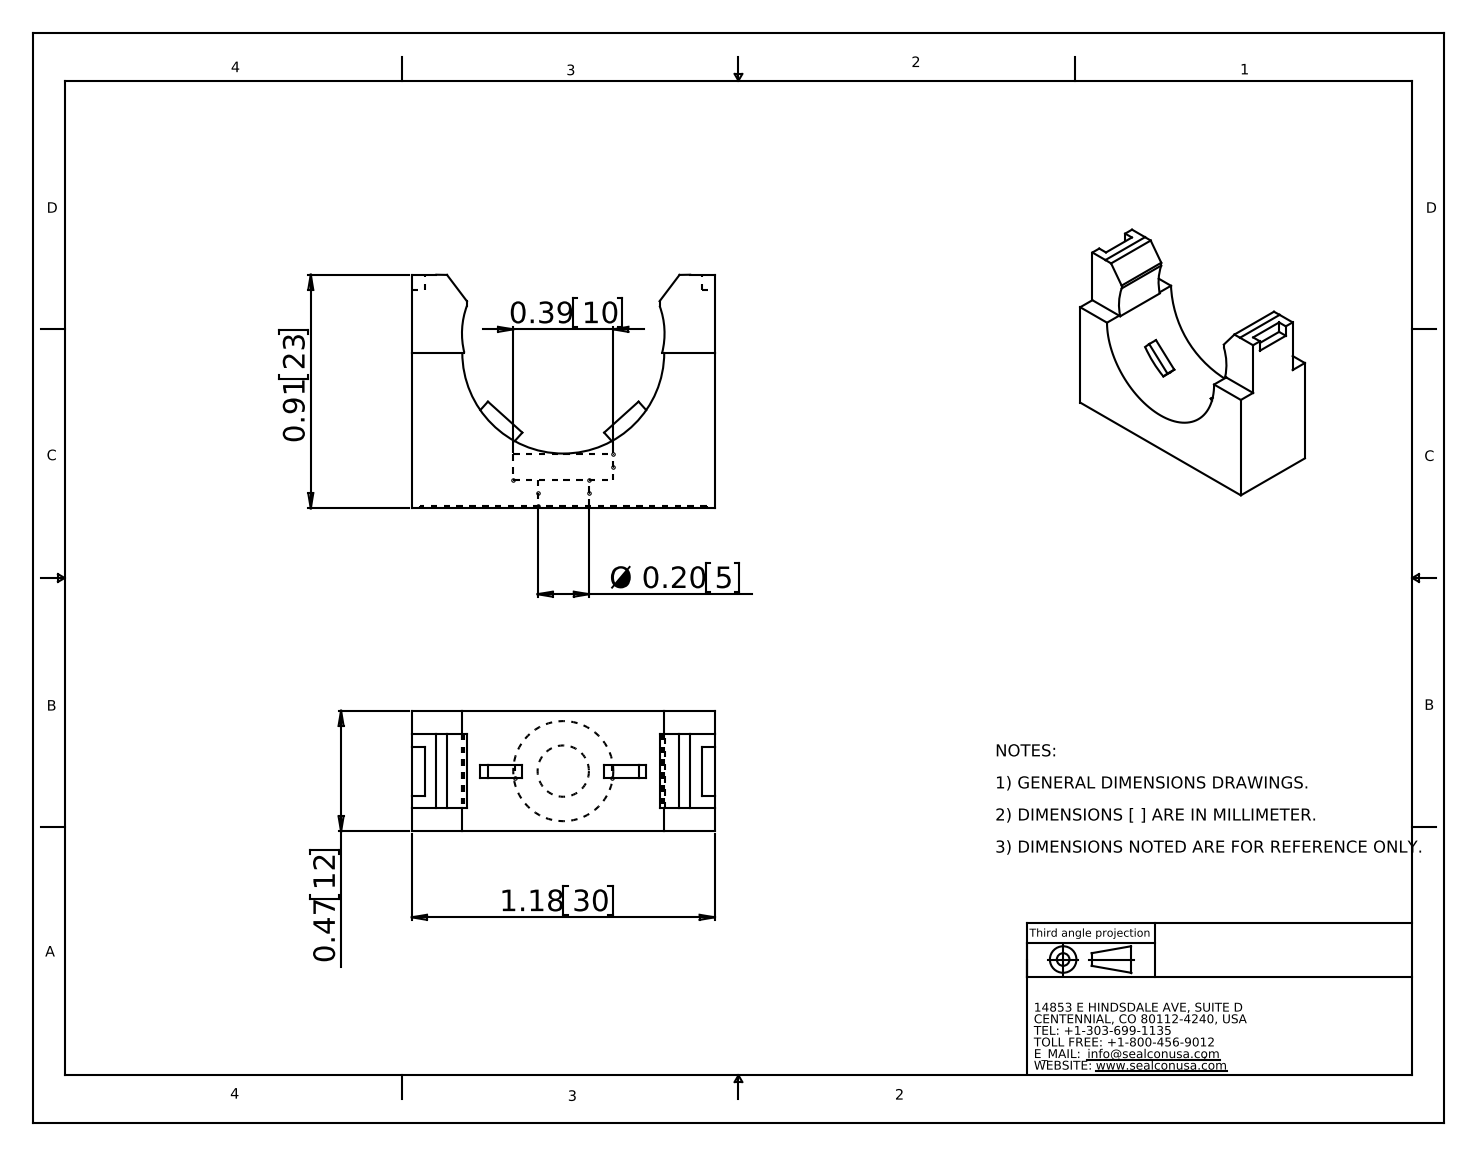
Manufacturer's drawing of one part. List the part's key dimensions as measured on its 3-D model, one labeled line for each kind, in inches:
Part name (STEP PRODUCT): MB-11-BK
STEP written by: SolidWorks 2008 (CONFIG_CONTROL_DESIGN)
Units: inches
Bodies: 1 solid, 56 faces (48 planar, 8 cylindrical, 0 other)
Overall size (bounding box): 1.18 × 0.91 × 0.47
Volume: 0.236 in³ · Surface area: 3.859 in²
Round holes (diameter × count): ⌀0.2 ×1, ⌀0.39 ×1
Partial cylindrical surfaces — rounded edges, fillets, slot ends (radius × count): R0.31 ×2, R0.393 ×1
Main face-to-face distances: 0.47, 1.18, 0.1, 0.2, 0.21, 0.089, 0.38, 0.291, 0.381, 0.09
